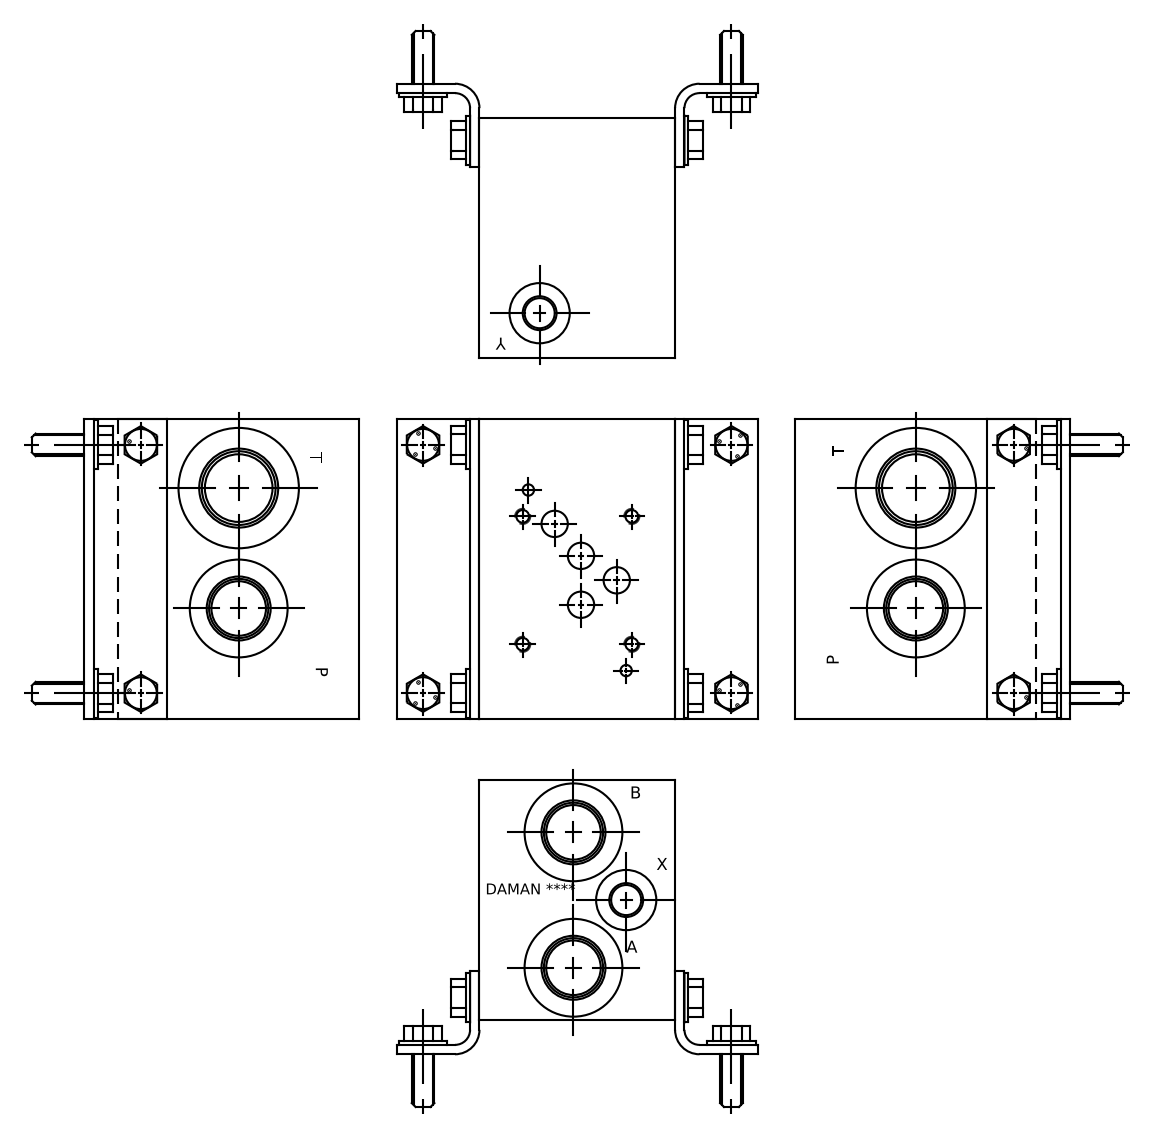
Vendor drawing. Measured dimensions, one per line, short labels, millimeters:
name: Part_AD05HP013S_13_3D
written by: Autodesk Inventor 2020 (AUTOMOTIVE_DESIGN)
unit: mm
bodies: 1 solid, 628 faces (360 planar, 63 cylindrical, 205 other)
size: 127 × 101.6 × 82.55
volume: 916 699 mm³; area: 87 103 mm²
holes: 4× ⌀5.11, 4× ⌀6.35, 3× ⌀11.11, 3× ⌀23.01, 3× ⌀24.92, 3× ⌀27.43, 3× ⌀42.04, 2× ⌀4.78, 2× ⌀7.92, 2× ⌀9.53, 2× ⌀12.29, 2× ⌀12.9
face distances: 101.6, 82.55, 0.79, 127, 81.76, 126.21, 80.97, 19.05, 19.84, 62.71
hole spacings: 18.29, 45.05, 11.35, 11.37, 13.89, 17.48, 18.11, 19.27
